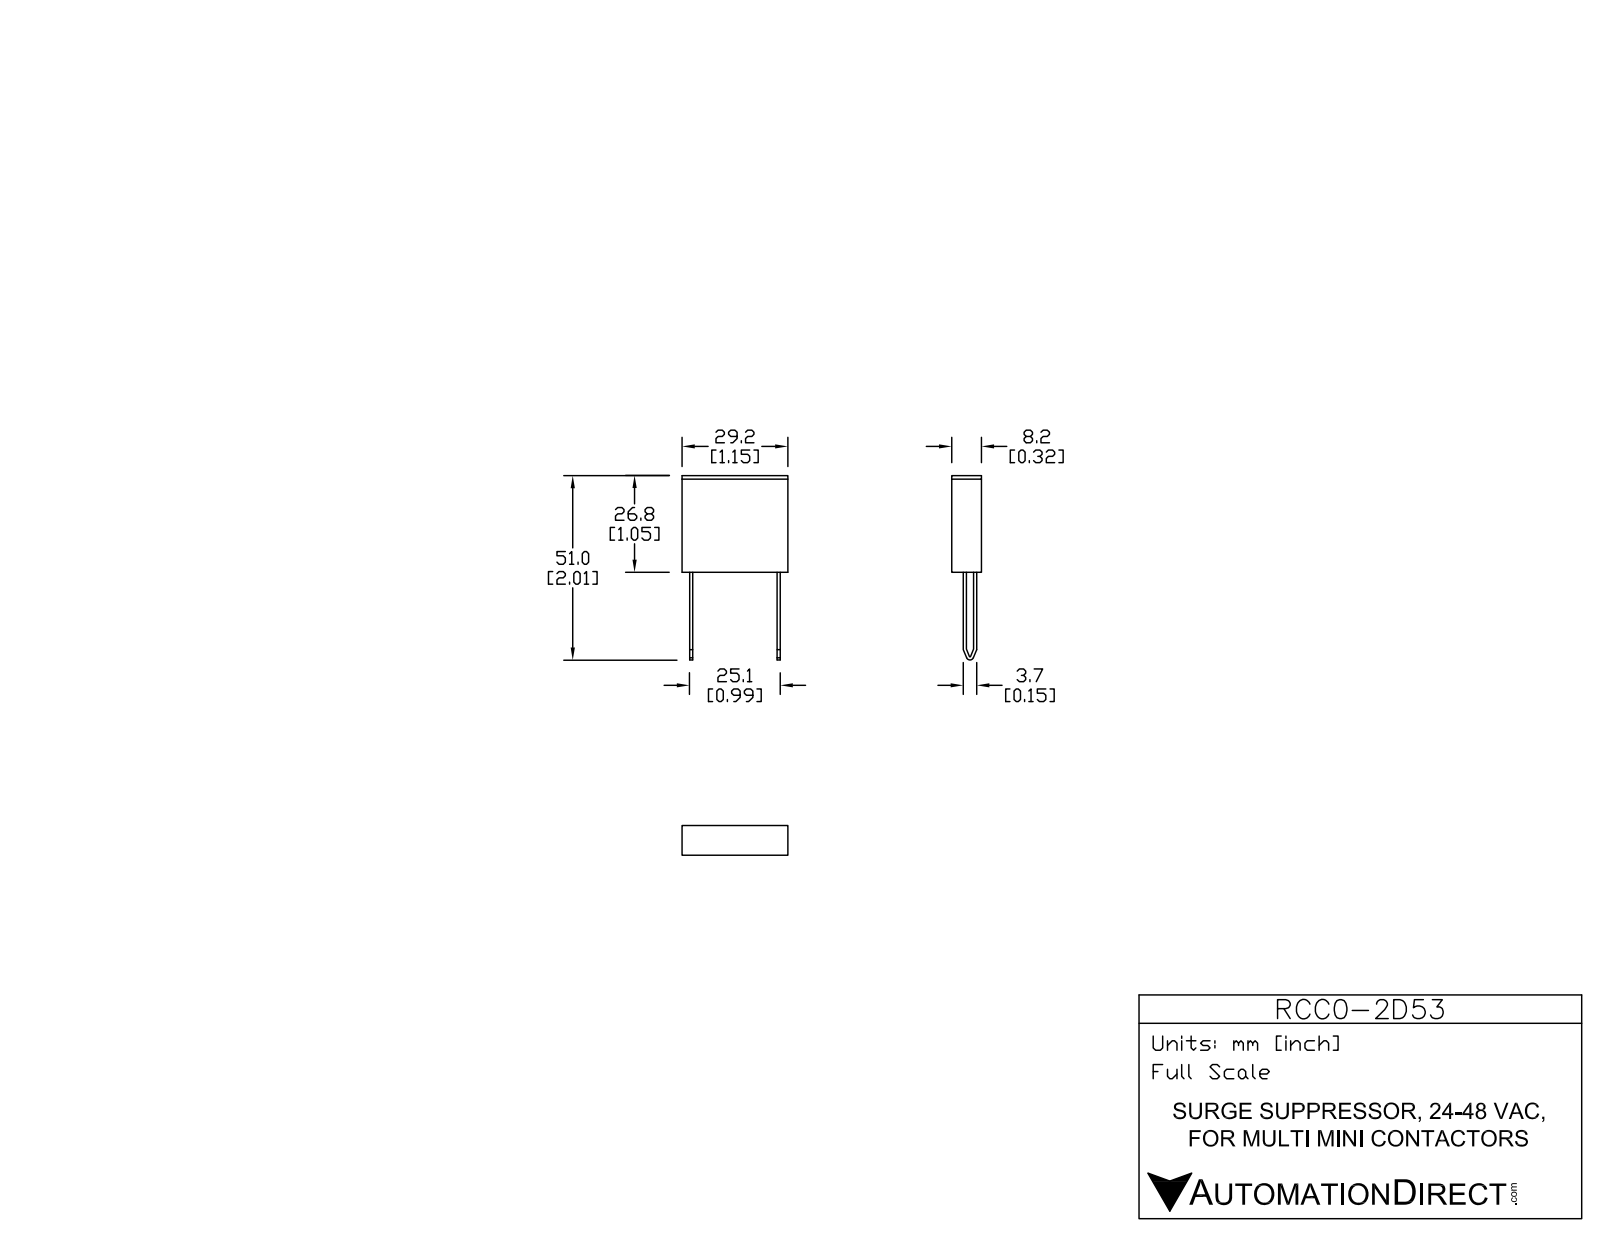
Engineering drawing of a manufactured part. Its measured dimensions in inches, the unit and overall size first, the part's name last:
Units: inches
Overall size (bounding box): 2.004 × 1.15 × 0.323
Partial cylindrical surfaces — rounded edges, fillets, slot ends (radius × count): R0.006 ×1, R0.039 ×1
Main face-to-face distances: 0.323, 1.051, 1.15, 0.033, 0.083, 1.067, 0.116, 1.033, 0.951, 0.112
Volume: 0.394 in³ · Surface area: 4.345 in²
Bodies: 1 solid, 34 faces (26 planar, 8 cylindrical, 0 other)
Part name (STEP PRODUCT): RCC0-2D53
STEP written by: SolidWorks 2013 (AUTOMOTIVE_DESIGN)
